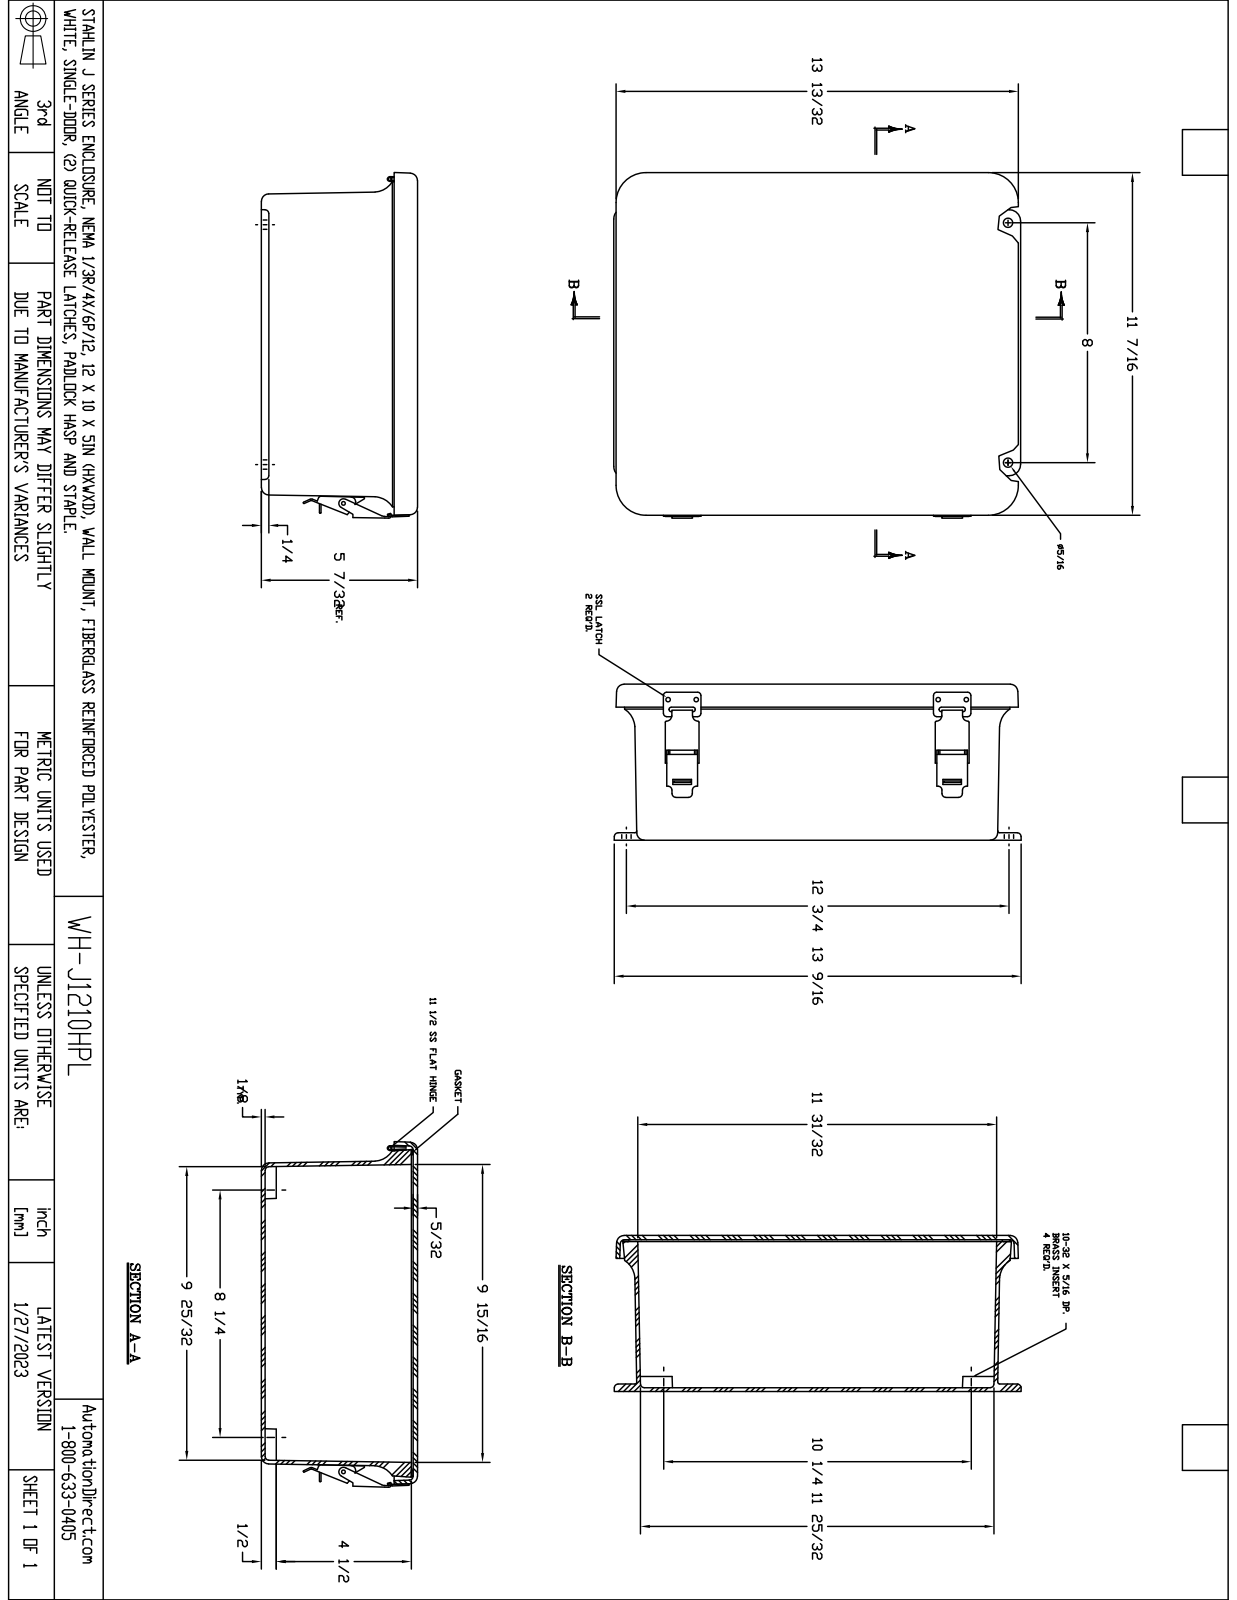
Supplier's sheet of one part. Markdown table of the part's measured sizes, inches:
| quantity | value |
| --- | --- |
| part name | WH-M1210HPL |
| STEP written by | SolidWorks 2018 (AUTOMOTIVE_DESIGN) |
| units | inches |
| bodies | 38 solids, 979 faces (423 planar, 409 cylindrical, 147 other) |
| overall size | 13.563 × 11.537 × 5.231 |
| volume | 87.3 in³ |
| surface area | 1 198 in² |
| round holes (diameter × count) | 0.14 × 20, 0.104 × 8, 0.131 × 8, 0.152 × 5, 0.13 × 4, 0.156 × 4, 0.218 × 4, 0.135 × 2, 0.375 × 2, 0.085 × 1, 0.085 × 1, 0.135 × 1 |
| round bosses / shafts (diameter × count) | 0.125 × 12, 0.25 × 8, 0.27 × 4, 0.125 × 4, 0.3 × 1, 0.17 × 1, 0.155 × 1, 0.12 × 1 |
| partial cylindrical surfaces (radius × count) | 0.015 × 20, 0.031 × 20, 0.125 × 20, 0.045 × 16, 0.03 × 12, 0.023 × 9, 0.25 × 8, 0.06 × 6 |
| main face-to-face distances | 0.143, 0.125, 5.088, 5.231, 4.963, 5.106, 5, 4.875, 0.088, 0.231 |
| hole center spacings | 9, 9.031, 0.937, 0.75, 3.625, 0.25, 0.75, 1.348 |
